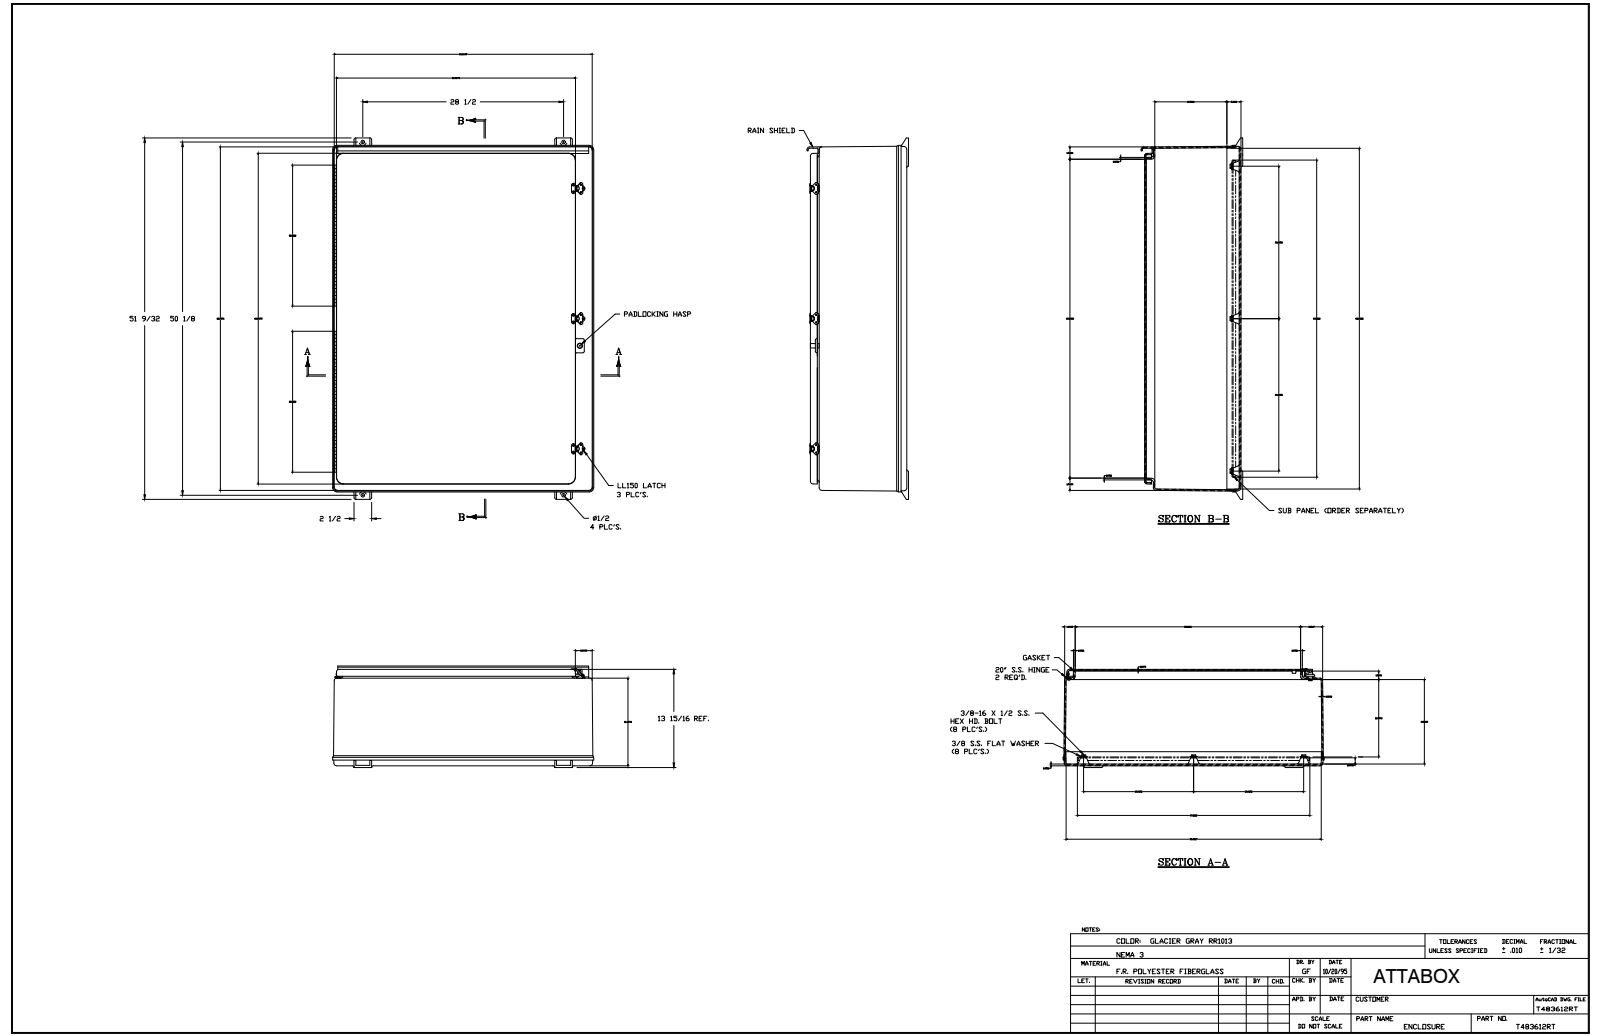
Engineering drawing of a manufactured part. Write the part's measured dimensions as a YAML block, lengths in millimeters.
part_name: "T483612RT"
step_written_by: "SolidWorks 2018 (AUTOMOTIVE_DESIGN)"
units: millimeters
bodies: {solids: 62, faces: 1702, planar: 671, cylindrical: 692, other: 339}
overall_size: [1302.5, 941.4, 367.1]
volume: 21940000
surface_area: 8411000
round_holes:
  - {diameter: 3.3, count: 41}
  - {diameter: 1.6, count: 12}
  - {diameter: 1.7, count: 10}
  - {diameter: 1.7, count: 9}
  - {diameter: 14.3, count: 8}
  - {diameter: 3.5, count: 6}
  - {diameter: 4.7, count: 6}
  - {diameter: 3.7, count: 2}
  - {diameter: 7.1, count: 2}
  - {diameter: 13, count: 2}
  - {diameter: 13, count: 2}
  - {diameter: 3.2, count: 1}
round_bosses_or_shafts:
  - {diameter: 7.5, count: 19}
  - {diameter: 3.6, count: 12}
  - {diameter: 12.7, count: 3}
  - {diameter: 6.4, count: 1}
  - {diameter: 5.1, count: 1}
  - {diameter: 5.1, count: 1}
  - {diameter: 3.4, count: 1}
partial_cylinders:
  - {radius: 0.3, count: 86}
  - {radius: 6.4, count: 24}
  - {radius: 9.5, count: 13}
  - {radius: 0.8, count: 12}
  - {radius: 4.7, count: 12}
  - {radius: 7.9, count: 12}
  - {radius: 12.7, count: 12}
  - {radius: 4.8, count: 10}
face_to_face_distances: [5.2, 6.4, 4.8, 347.3, 340.9, 342.5, 336.2, 316.3, 310, 26.2]
hole_center_spacings: [469.1, 598.5, 161.9, 161.9, 320.7, 320.7, 158.8, 482.6]
